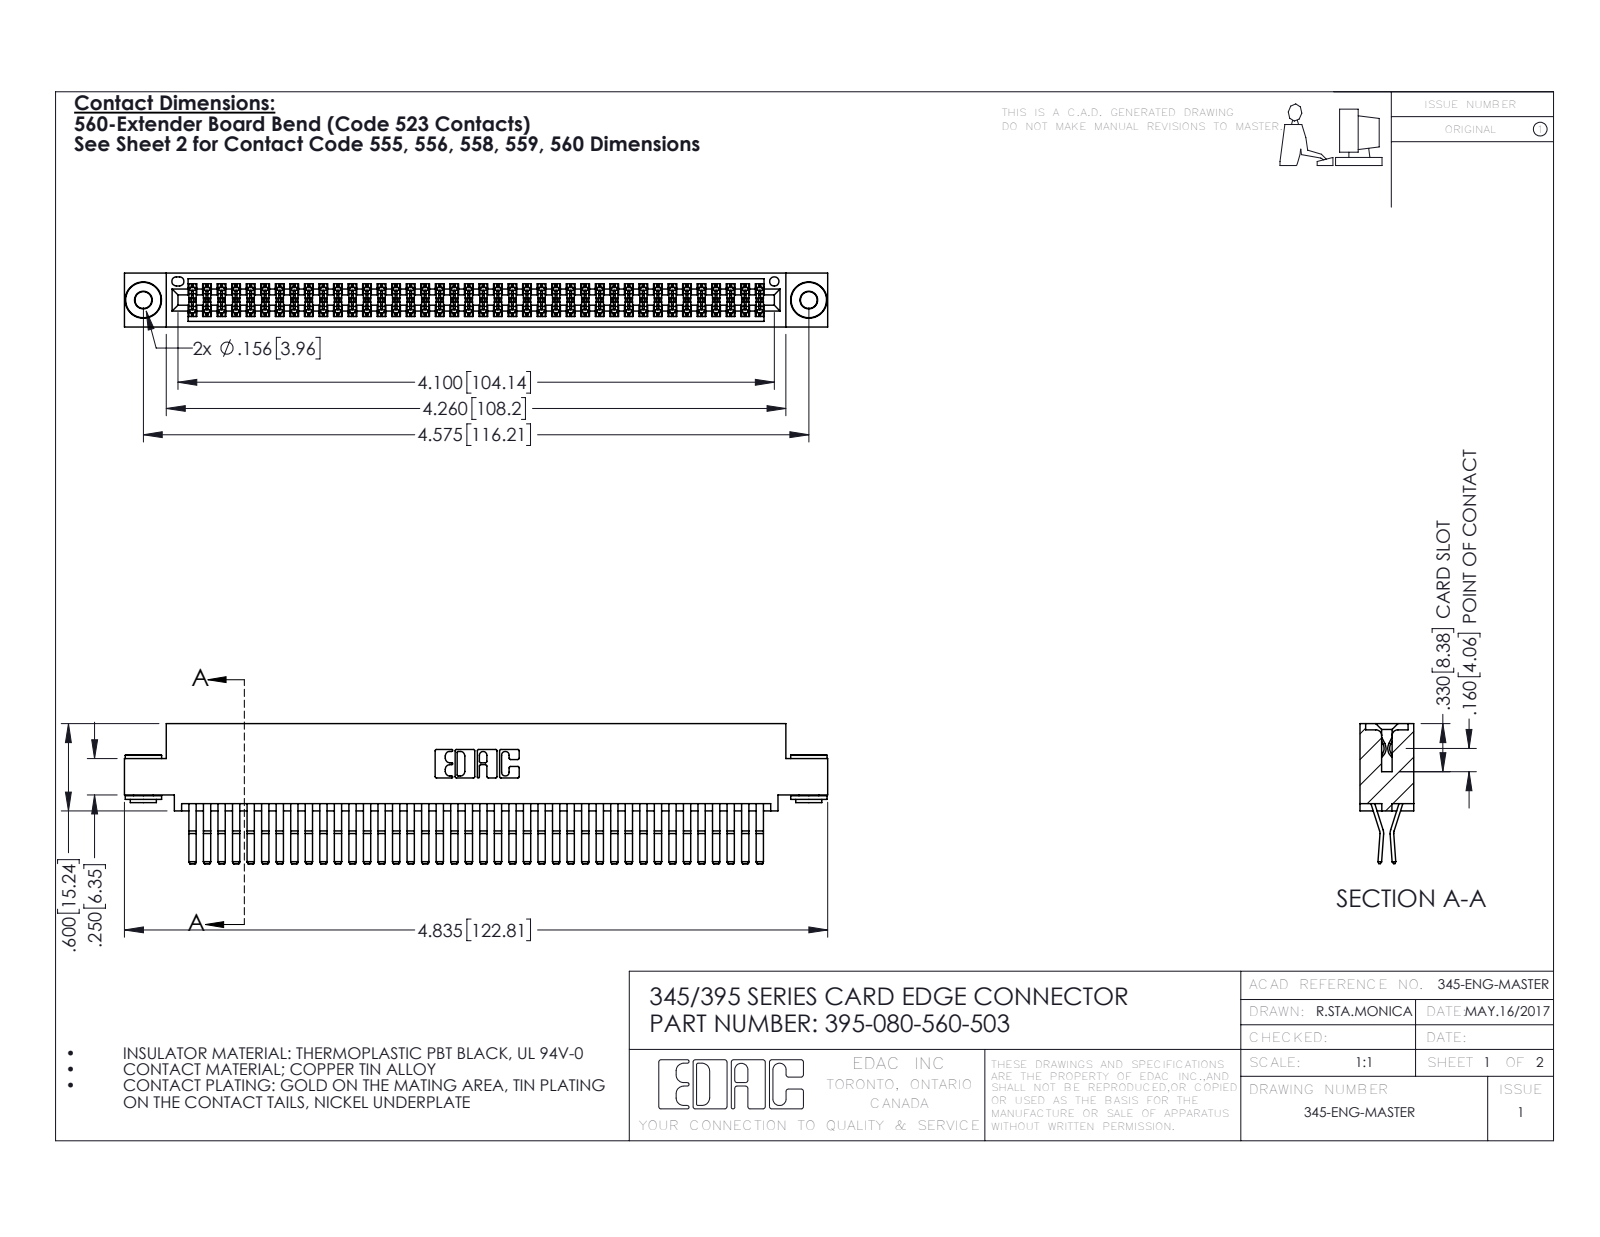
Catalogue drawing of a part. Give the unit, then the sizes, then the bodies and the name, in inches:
Units: inches
Overall size (bounding box): 4.835 × 0.962 × 0.37
Round holes (diameter × count): ⌀0.116 ×2, ⌀0.156 ×2, ⌀0.064 ×1
Round bosses / shafts (diameter × count): ⌀0.25 ×2, ⌀0.18 ×2, ⌀0.136 ×2
Partial cylindrical surfaces — rounded edges, fillets, slot ends (radius × count): R0.006 ×120, R0.01 ×22, R0.007 ×6, R0.031 ×6, R0.026 ×3, R0.01 ×2, R0.014 ×2, R0.019 ×2
Main face-to-face distances: 0.025, 0.072, 0.298, 0.37, 0.2, 0.098, 0.272, 0.225, 0.175, 0.149
Hole centre spacings: 0.27, 4.339, 4.575
Volume: 0.756 in³ · Surface area: 30.86 in²
Bodies: 83 solids, 4328 faces (2734 planar, 1586 cylindrical, 8 other)
Part name (STEP PRODUCT): 395-080-560-503; 345-250-002_345-250-002-102; 345-292-001_560 Tail; 345 Part_0.110 Offset - 0.156 Dia-TH
STEP written by: SolidWorks 2016 (CONFIG_CONTROL_DESIGN)
